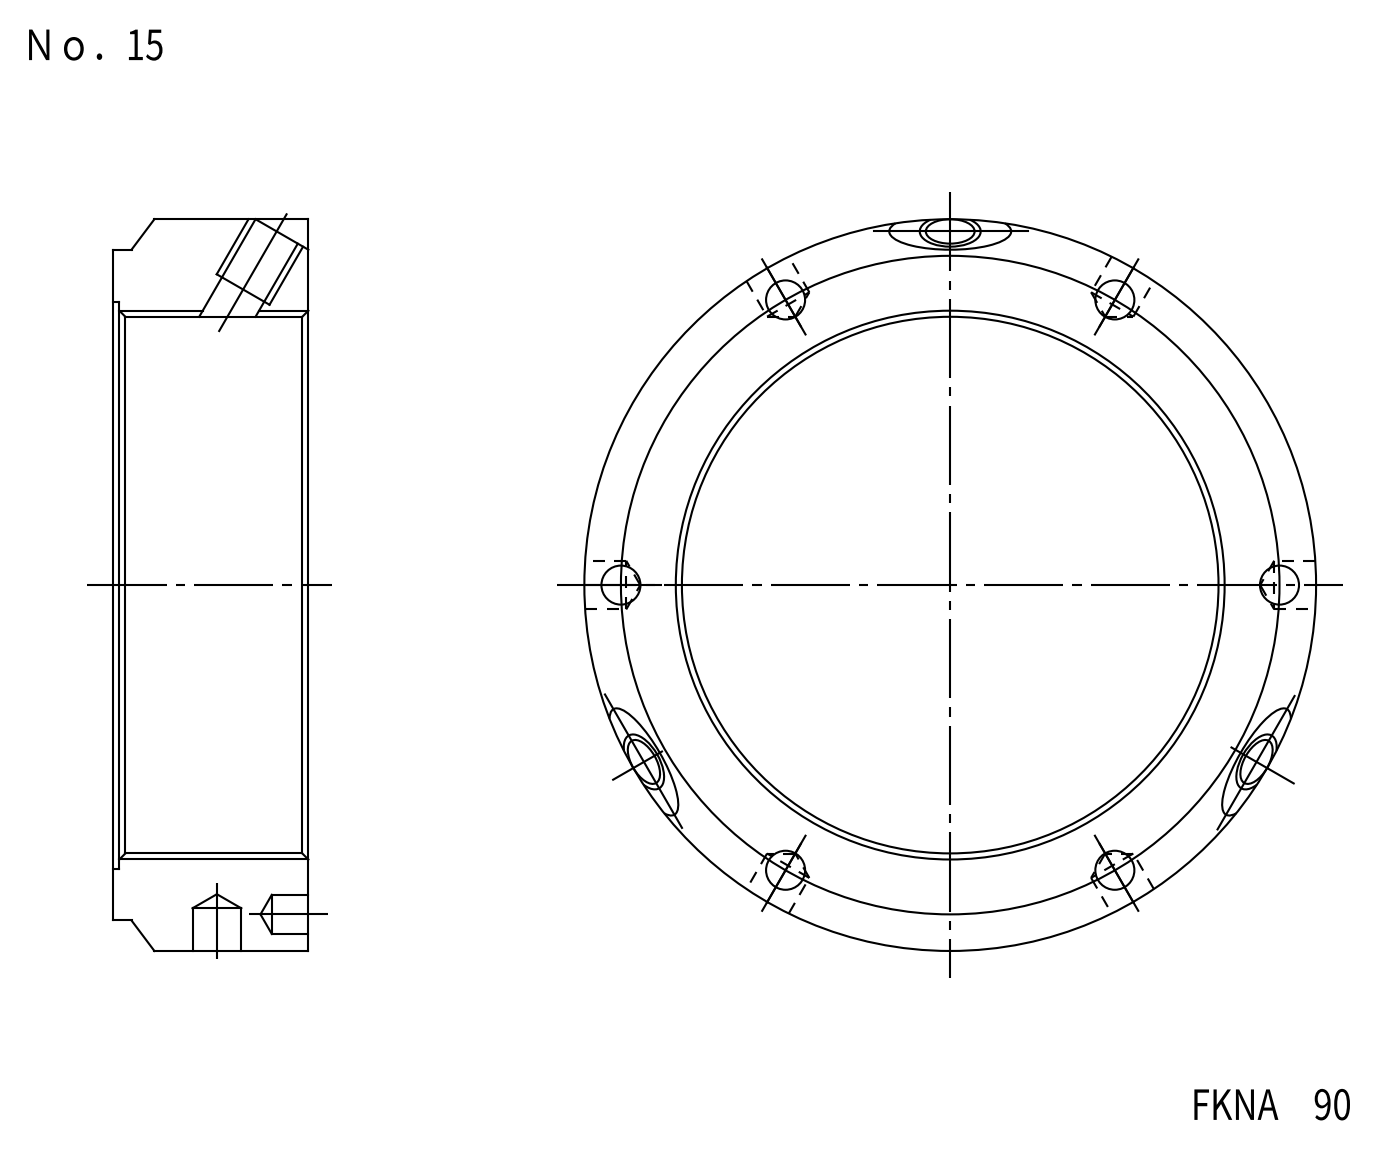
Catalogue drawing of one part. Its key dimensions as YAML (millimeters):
part_name: "FKD FKNA90"
step_written_by: "Autodesk Inventor LT (CONFIG_CONTROL_DESIGN)"
units: millimeters
bodies: {solids: 1, faces: 44, planar: 6, cylindrical: 25, other: 13}
overall_size: [120, 120, 32]
volume: 146405
surface_area: 32425
round_holes:
  - {diameter: 6.4, count: 6}
  - {diameter: 8, count: 3}
  - {diameter: 8.38, count: 3}
  - {diameter: 10.2, count: 3}
  - {diameter: 90, count: 1}
  - {diameter: 93, count: 1}
round_bosses_or_shafts:
  - {diameter: 120, count: 1}
  - {diameter: 110, count: 1}
partial_cylinders:
  - {radius: 20, count: 3}
face_to_face_distances: [32, 1.5, 30.5]
hole_center_spacings: [54, 93.53, 93.54, 108.01, 108]
